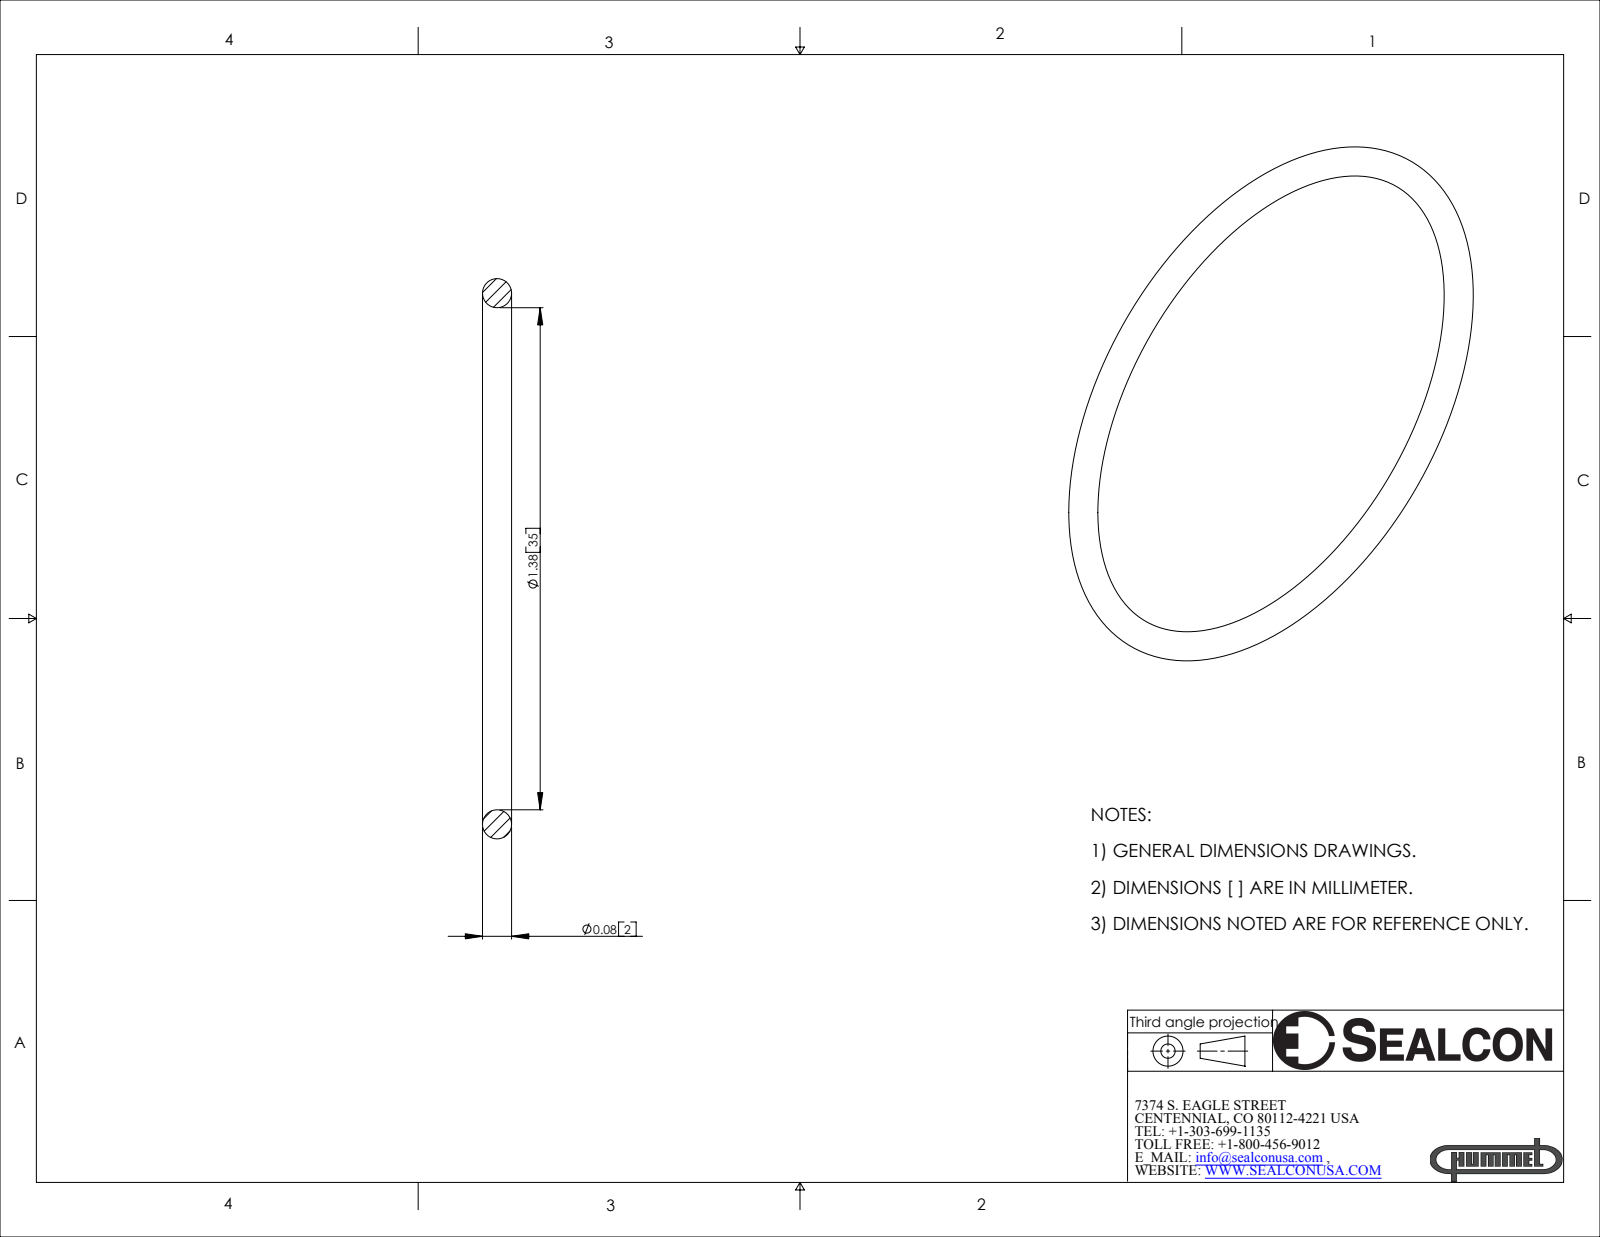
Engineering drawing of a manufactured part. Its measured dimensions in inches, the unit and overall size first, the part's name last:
Units: inches
Overall size (bounding box): 1.54 × 1.54 × 0.08
Volume: 0.023 in³ · Surface area: 1.153 in²
Bodies: 1 solid, 4 faces (0 planar, 0 cylindrical, 4 other)
Part name (STEP PRODUCT): OM-40-BN
STEP written by: SolidWorks 2007 (CONFIG_CONTROL_DESIGN)
